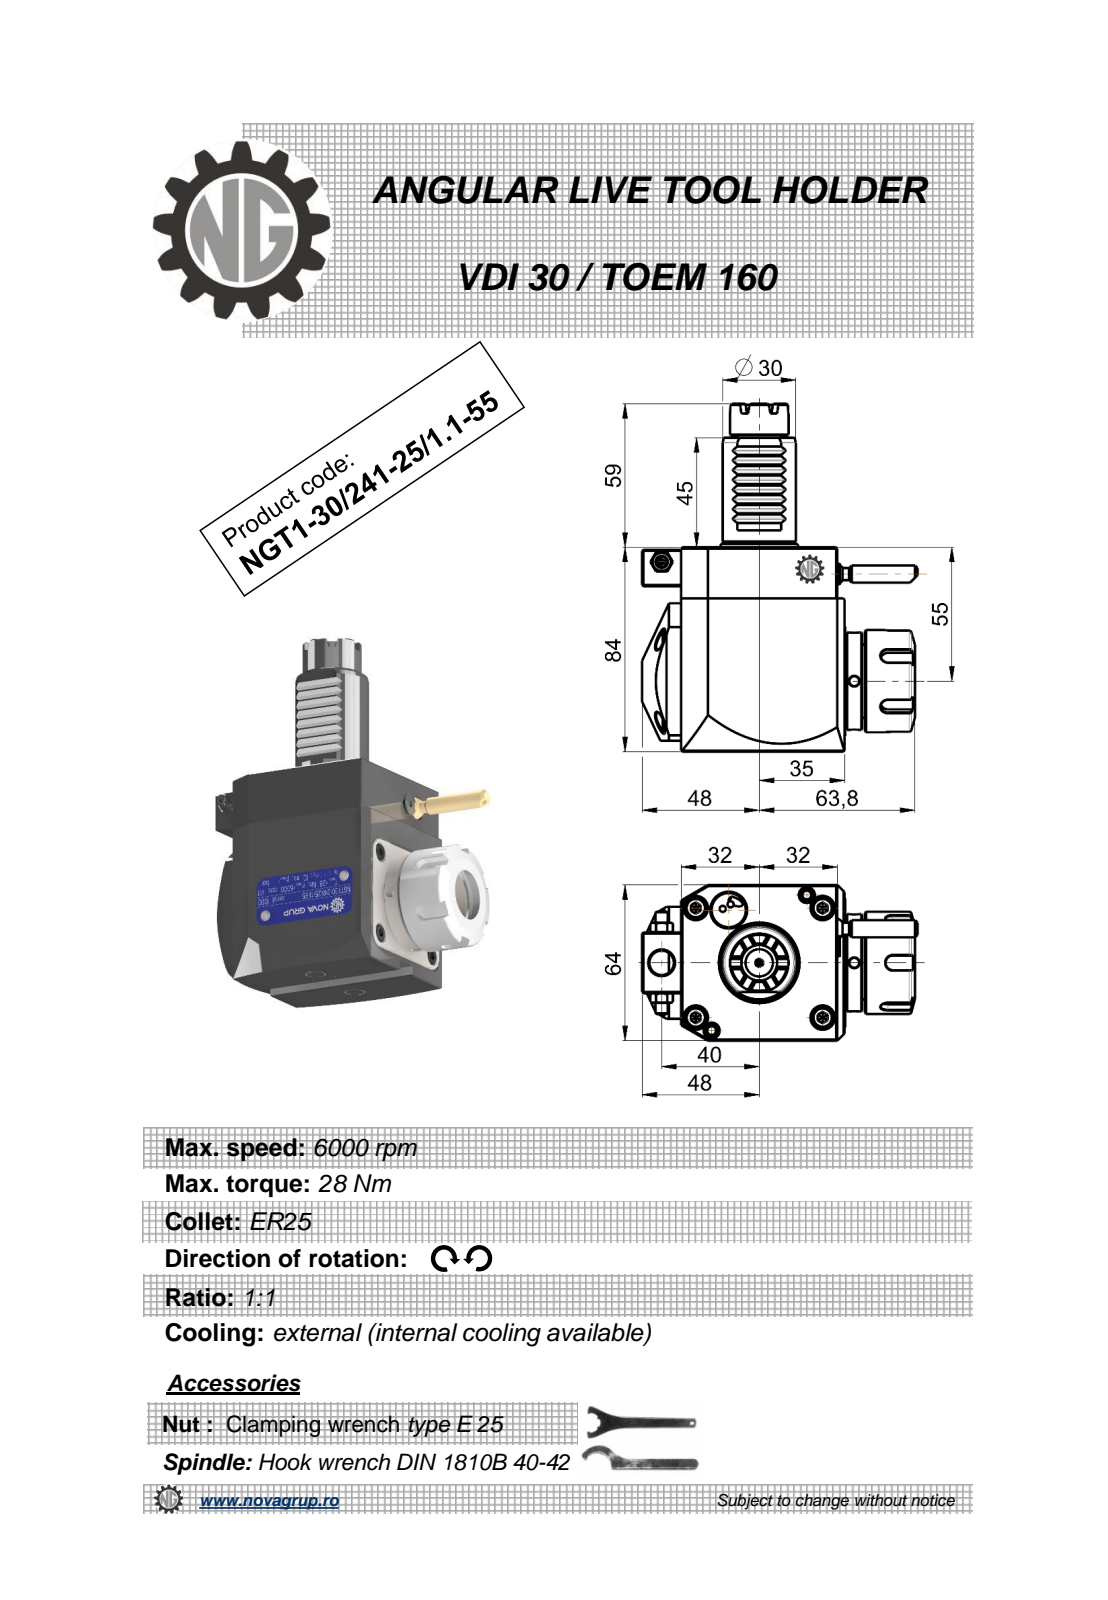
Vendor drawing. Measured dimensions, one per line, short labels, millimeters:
name: NGT1_30_241_25_1_1_55
written by: PRO/ENGINEER BY PARAMETRIC TECHNOLOGY CORPORATION, 2010280 (CONFIG_CONTROL_DESIGN)
unit: mm
bodies: 1 solid, 457 faces (212 planar, 90 cylindrical, 155 other)
size: 143 × 112.88 × 65.6
volume: 448 741 mm³; area: 46 304 mm²
holes: 2× ⌀4, 1× ⌀2.5, 1× ⌀3, 1× ⌀4.2, 1× ⌀9.5, 1× ⌀10, 1× ⌀20.3
bosses: 2× ⌀8.96, 2× ⌀5, 1× ⌀42, 1× ⌀40, 1× ⌀33, 1× ⌀30, 1× ⌀24, 1× ⌀17.7
rounds: 12× R0.26, 8× R0.3, 5× R3, 4× R3.5, 2× R160, 1× R32
face distances: 64, 84, 67.2, 67, 80, 3.2, 3, 83, 16, 0.5
hole spacings: 14.22, 46.17, 46.5, 78.95, 92.92
